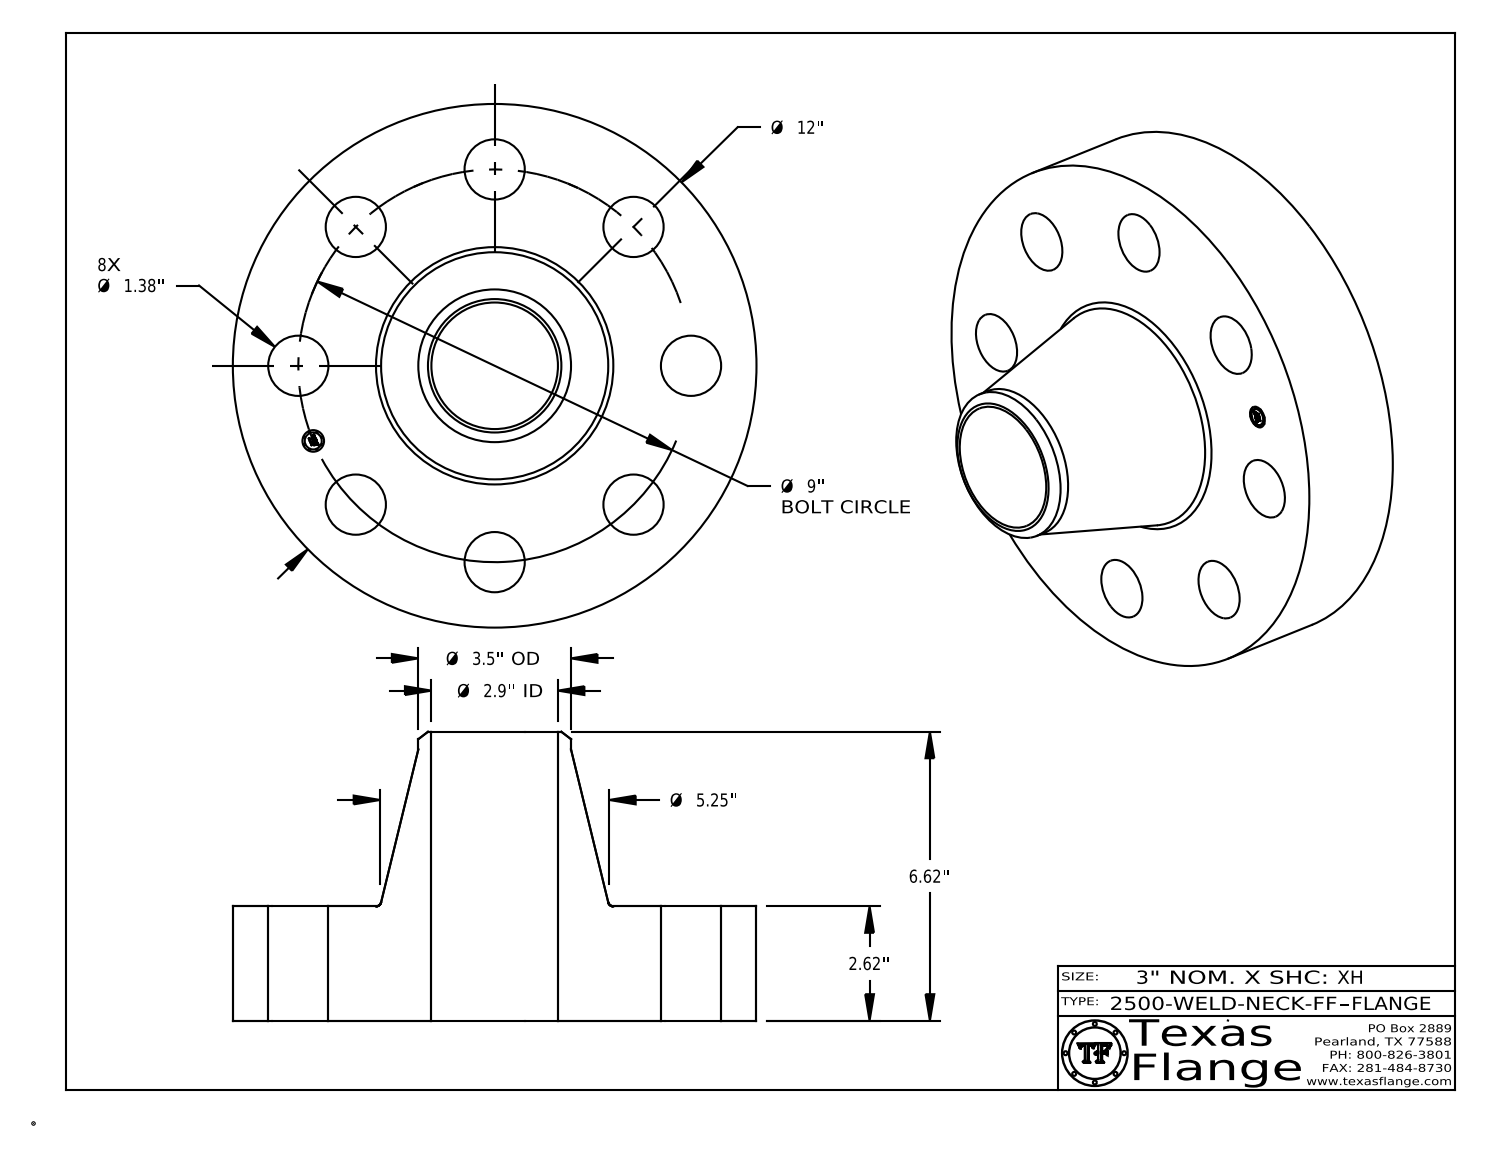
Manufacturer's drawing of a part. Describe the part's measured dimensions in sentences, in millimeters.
The part is named "2500-WELD-NECK-FF". Its 3-D file was written by "CATIA V5 STEP AP214 (AUTOMOTIVE_DESIGN)". It is 1 solid with 416 faces: 368 planar, 42 cylindrical and 6 other. Overall it measures 304.8 by 304.8 by 168.1 millimeters. Its volume is 4 583 000 cubic millimeters and its surface area 310 100 square millimeters. Round holes: 8 of diameter 35.1, 1 of diameter 12.6, 1 of diameter 73.7. Round bosses or shafts: 8 of diameter 0.8, 1 of diameter 304.8, 1 of diameter 88.9, 1 of diameter 9.9. The main face-to-face distances are 66.5, 168.1, 101.6, 66.2, 0.4, 102, 3.8, 3.7, 0.7, 2.4. The hole center spacings are 114.3, 87.5, 161.6, 211.2, 44.6, 127, 190.1, 228.6.
